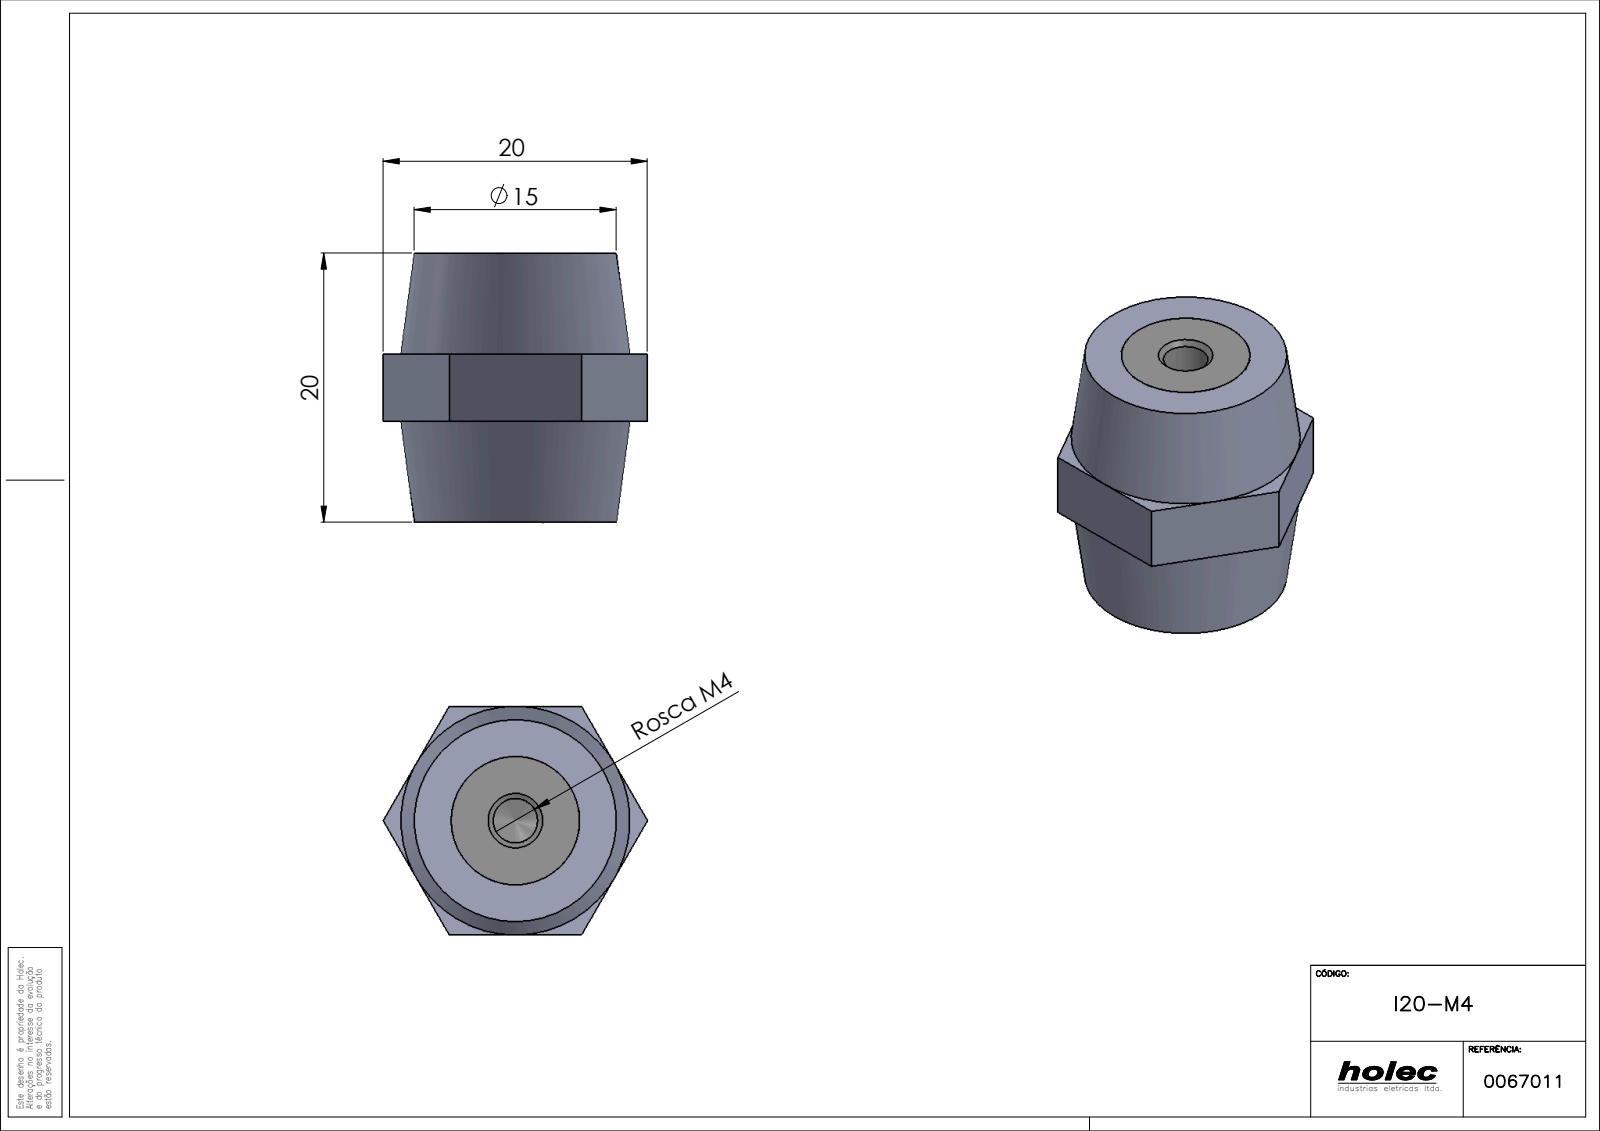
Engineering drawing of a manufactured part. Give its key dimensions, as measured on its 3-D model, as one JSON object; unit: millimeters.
{"part_name": "PB1_0100(PB1_0100_06)-1; I20-M4; PB1_0006-1", "step_written_by": "SolidWorks 2017 (AUTOMOTIVE_DESIGN)", "units": "millimeters", "bodies": {"solids": 3, "faces": 162, "planar": 82, "cylindrical": 12, "other": 68}, "overall_size": [20, 19.63, 17], "volume_mm3": 4183, "surface_area_mm2": 2843, "round_holes": [[3.3, 1], [8, 1]], "face_to_face_distances": [3.74, 13.26, 9.52, 6.5, 20, 17, 6.49, 13.51, 13.5, 7.01]}
